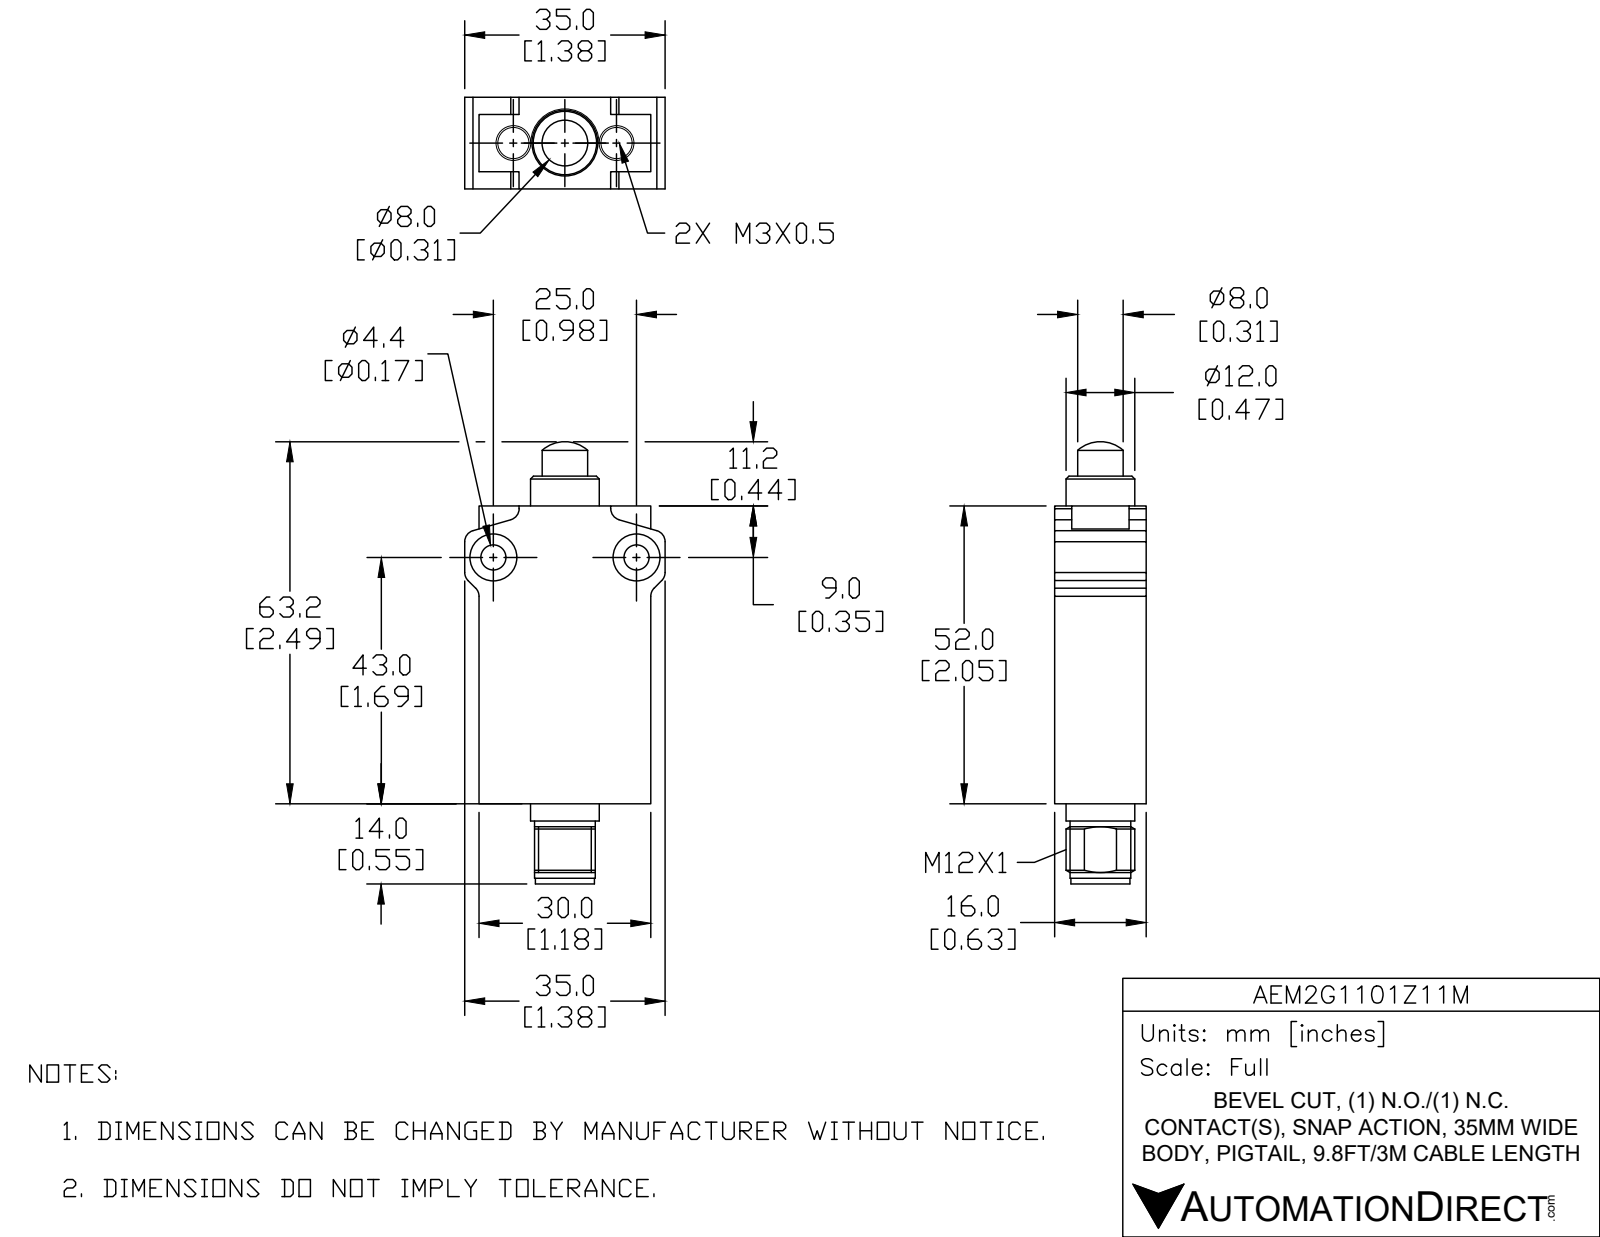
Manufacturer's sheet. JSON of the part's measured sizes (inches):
{"part_name": "AEM2G1101Z11M", "step_written_by": "SolidWorks 2018 (AUTOMOTIVE_DESIGN)", "units": "inches", "bodies": {"solids": 3, "faces": 99, "planar": 50, "cylindrical": 33, "other": 16}, "overall_size": [3.039, 1.378, 0.63], "volume_in3": 1.617, "surface_area_in2": 13.21, "round_holes": [[0.173, 2], [0.323, 2], [0.317, 1]], "round_bosses_or_shafts": [[0.472, 1], [0.417, 1], [0.406, 1], [0.313, 1]], "partial_cylinders_radius": [[0.079, 8], [0.256, 1]], "face_to_face_distances": [0.63, 1.181, 2.047, 0.472, 1.858, 0.189, 0.157, 0.098, 1.28, 0.039], "hole_center_spacings": [0.984]}
